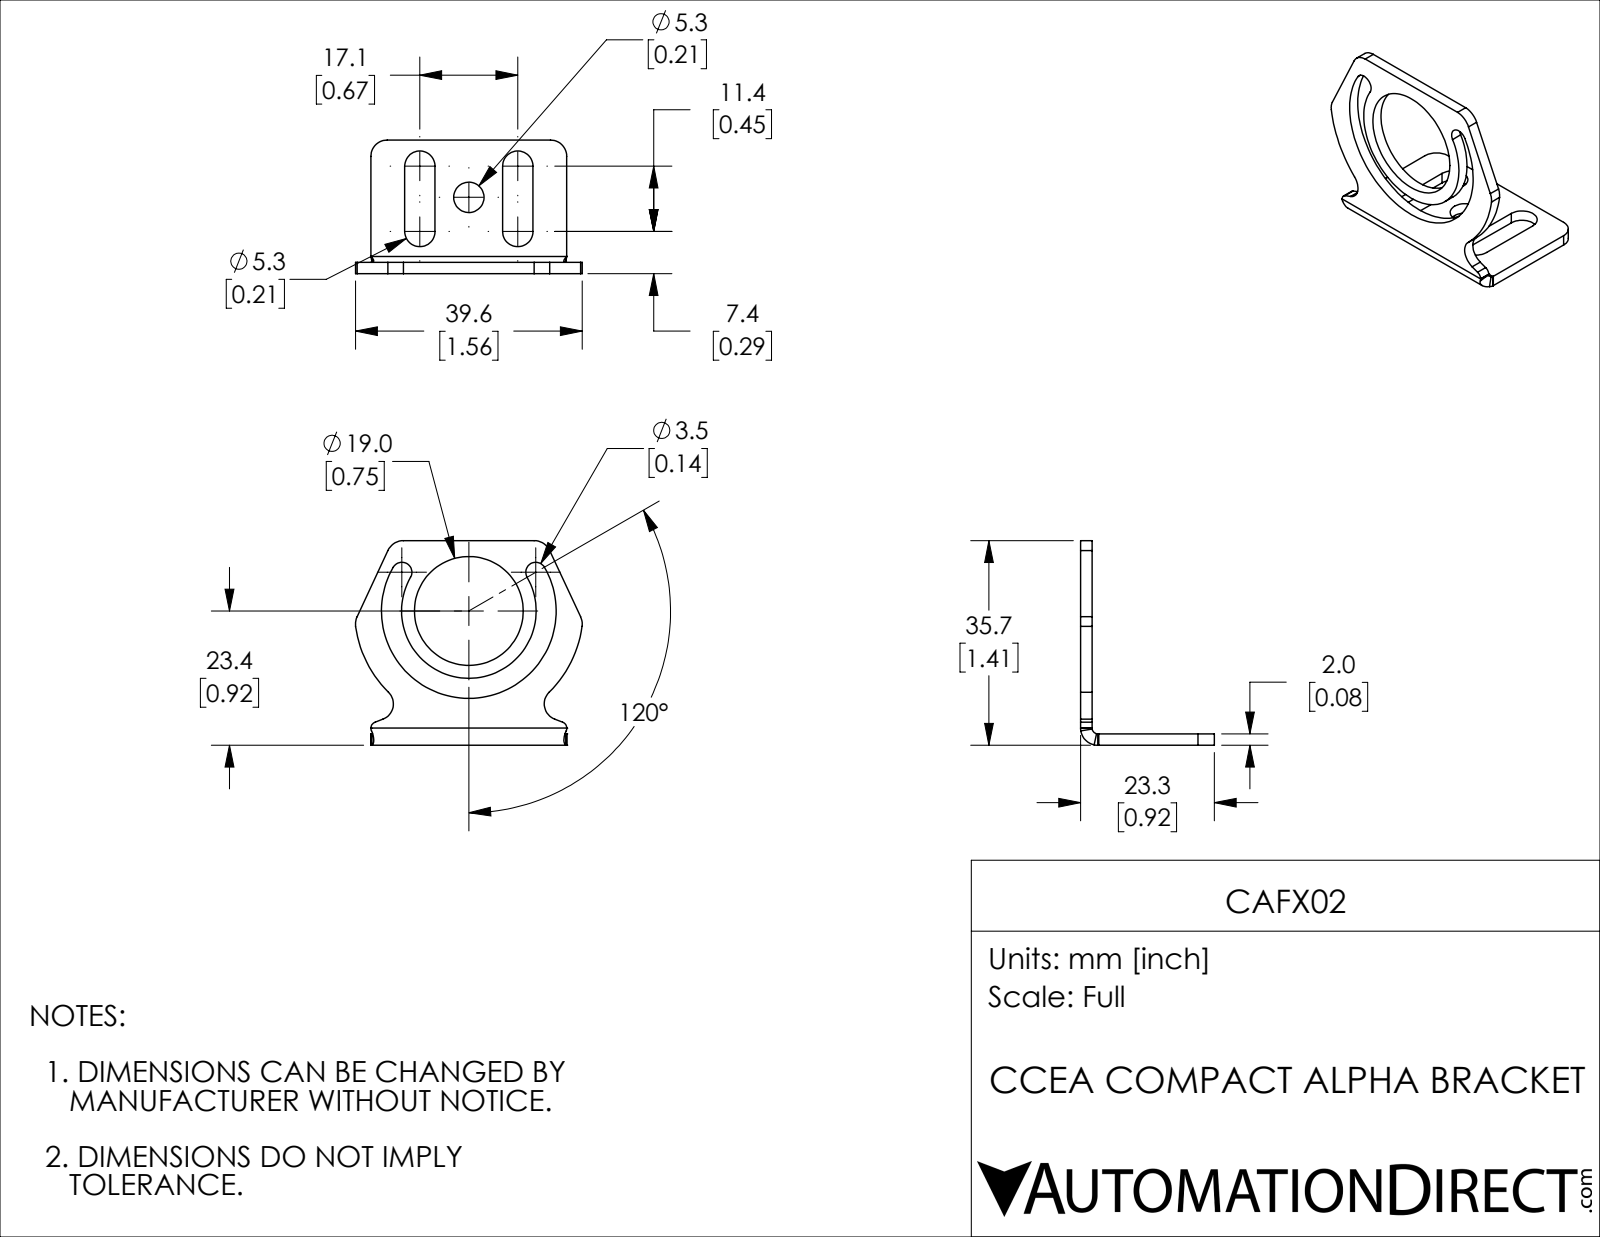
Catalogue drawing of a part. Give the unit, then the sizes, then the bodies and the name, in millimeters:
Units: millimetres
Overall size (bounding box): 39.6 × 35.7 × 23.3
Round holes (diameter × count): ⌀5.3 ×1, ⌀19 ×1
Partial cylindrical surfaces — rounded edges, fillets, slot ends (radius × count): R3 ×5, R2.6 ×4, R2.8 ×4, R1 ×3, R1.1 ×2, R1.8 ×2, R11.8 ×1, R15.2 ×1
Main face-to-face distances: 2, 21.3, 23.3, 33.7, 35.7, 5.9, 28.3, 11.2, 23, 5.3
Volume: 2 410 mm³ · Surface area: 3 334 mm²
Bodies: 1 solid, 54 faces (16 planar, 30 cylindrical, 8 other)
Part name (STEP PRODUCT): CAFX02
STEP written by: SolidWorks 2021 (CONFIG_CONTROL_DESIGN)
